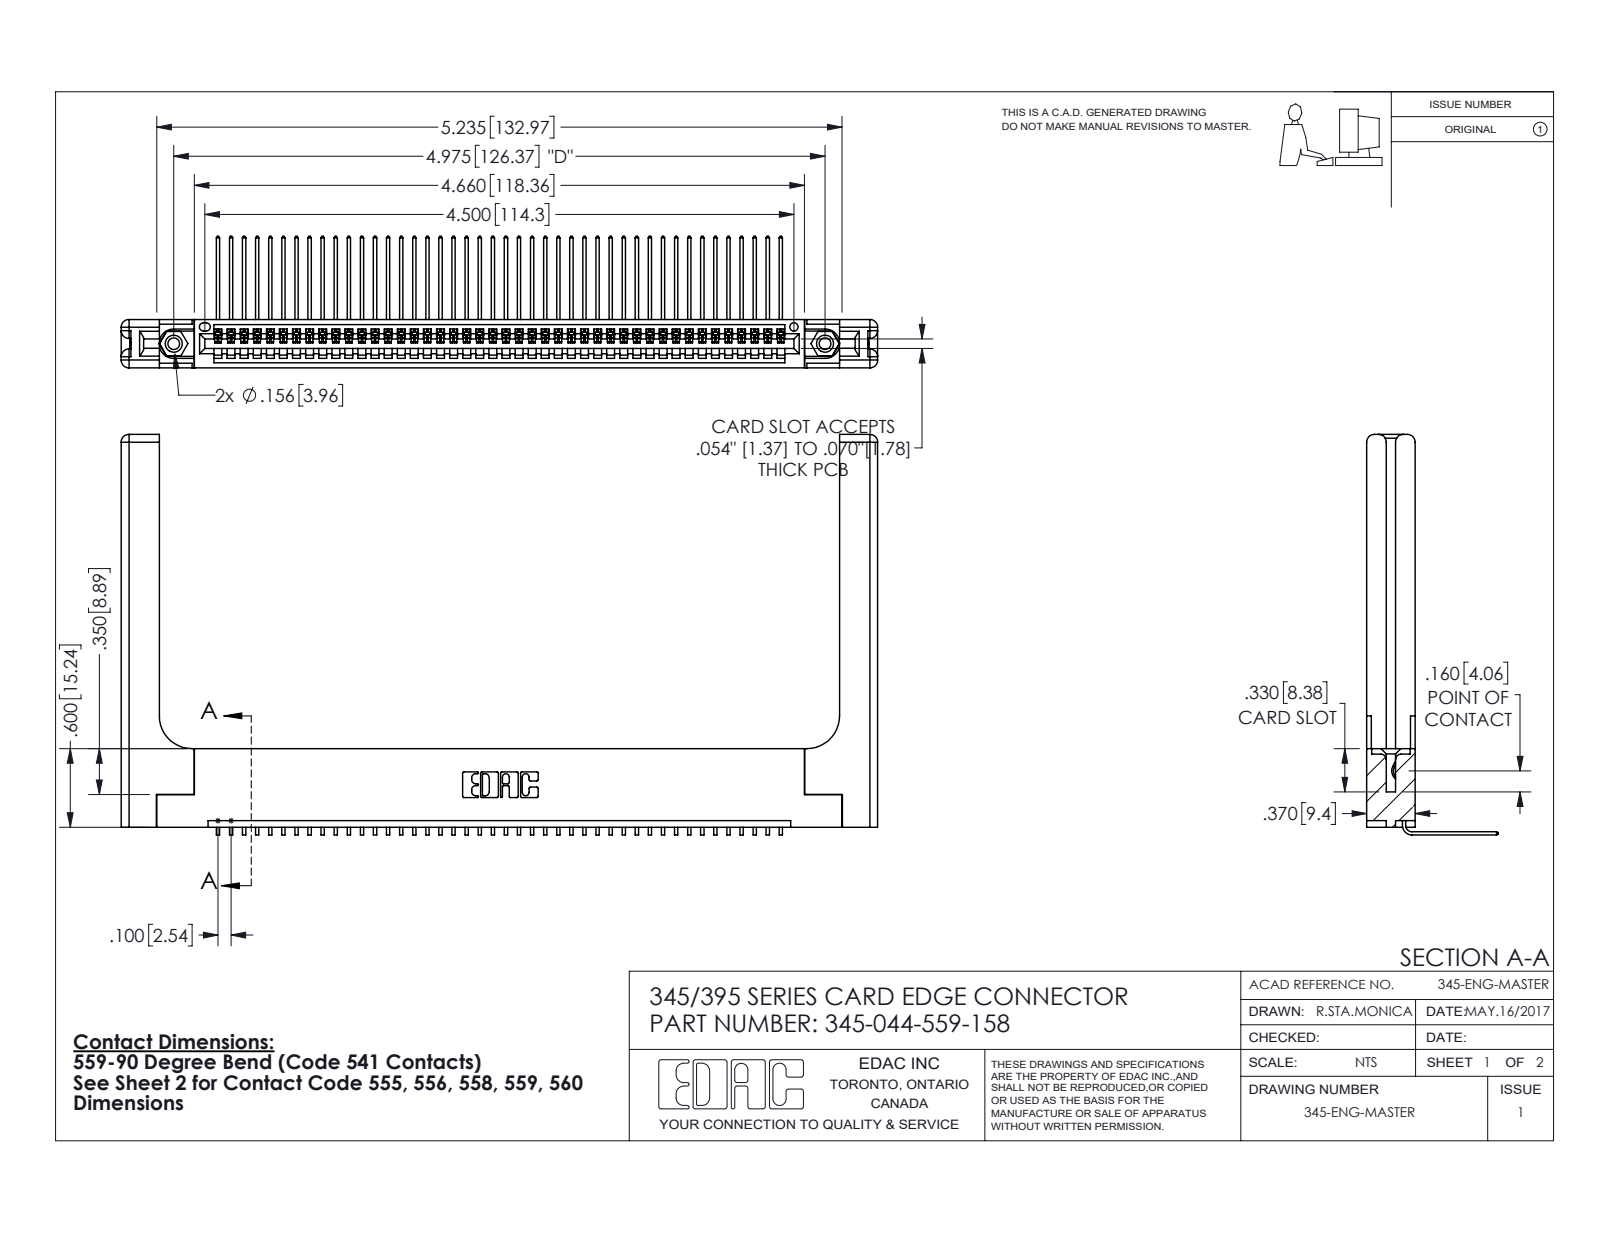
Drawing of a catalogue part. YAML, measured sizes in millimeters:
part_name: "345-220-058_345-220-058; 345 Part_Flush Mounting Lugs - 0.156 Dia-TH; 345-250-001_345-250-001-102; 345-044-559-158 (+1 more)"
step_written_by: "SolidWorks 2016 (CONFIG_CONTROL_DESIGN)"
units: millimeters
bodies: {solids: 49, faces: 3022, planar: 2076, cylindrical: 886, other: 60}
overall_size: [146.8, 77.7, 25.5]
volume: 22610
surface_area: 24940
round_holes:
  - {diameter: 2.3, count: 2}
  - {diameter: 3.2, count: 2}
  - {diameter: 4, count: 2}
  - {diameter: 1.6, count: 1}
round_bosses_or_shafts:
  - {diameter: 3.9, count: 2}
partial_cylinders:
  - {radius: 0.2, count: 88}
  - {radius: 0.3, count: 22}
  - {radius: 1.5, count: 16}
  - {radius: 0.2, count: 6}
  - {radius: 0.8, count: 6}
  - {radius: 0.7, count: 3}
  - {radius: 0.8, count: 2}
  - {radius: 0.8, count: 2}
face_to_face_distances: [9.4, 1.8, 7.6, 5.1, 2.5, 6.9, 0.6, 5.7, 3.8, 3.8]
hole_center_spacings: [6.9, 120.4, 126.4]
